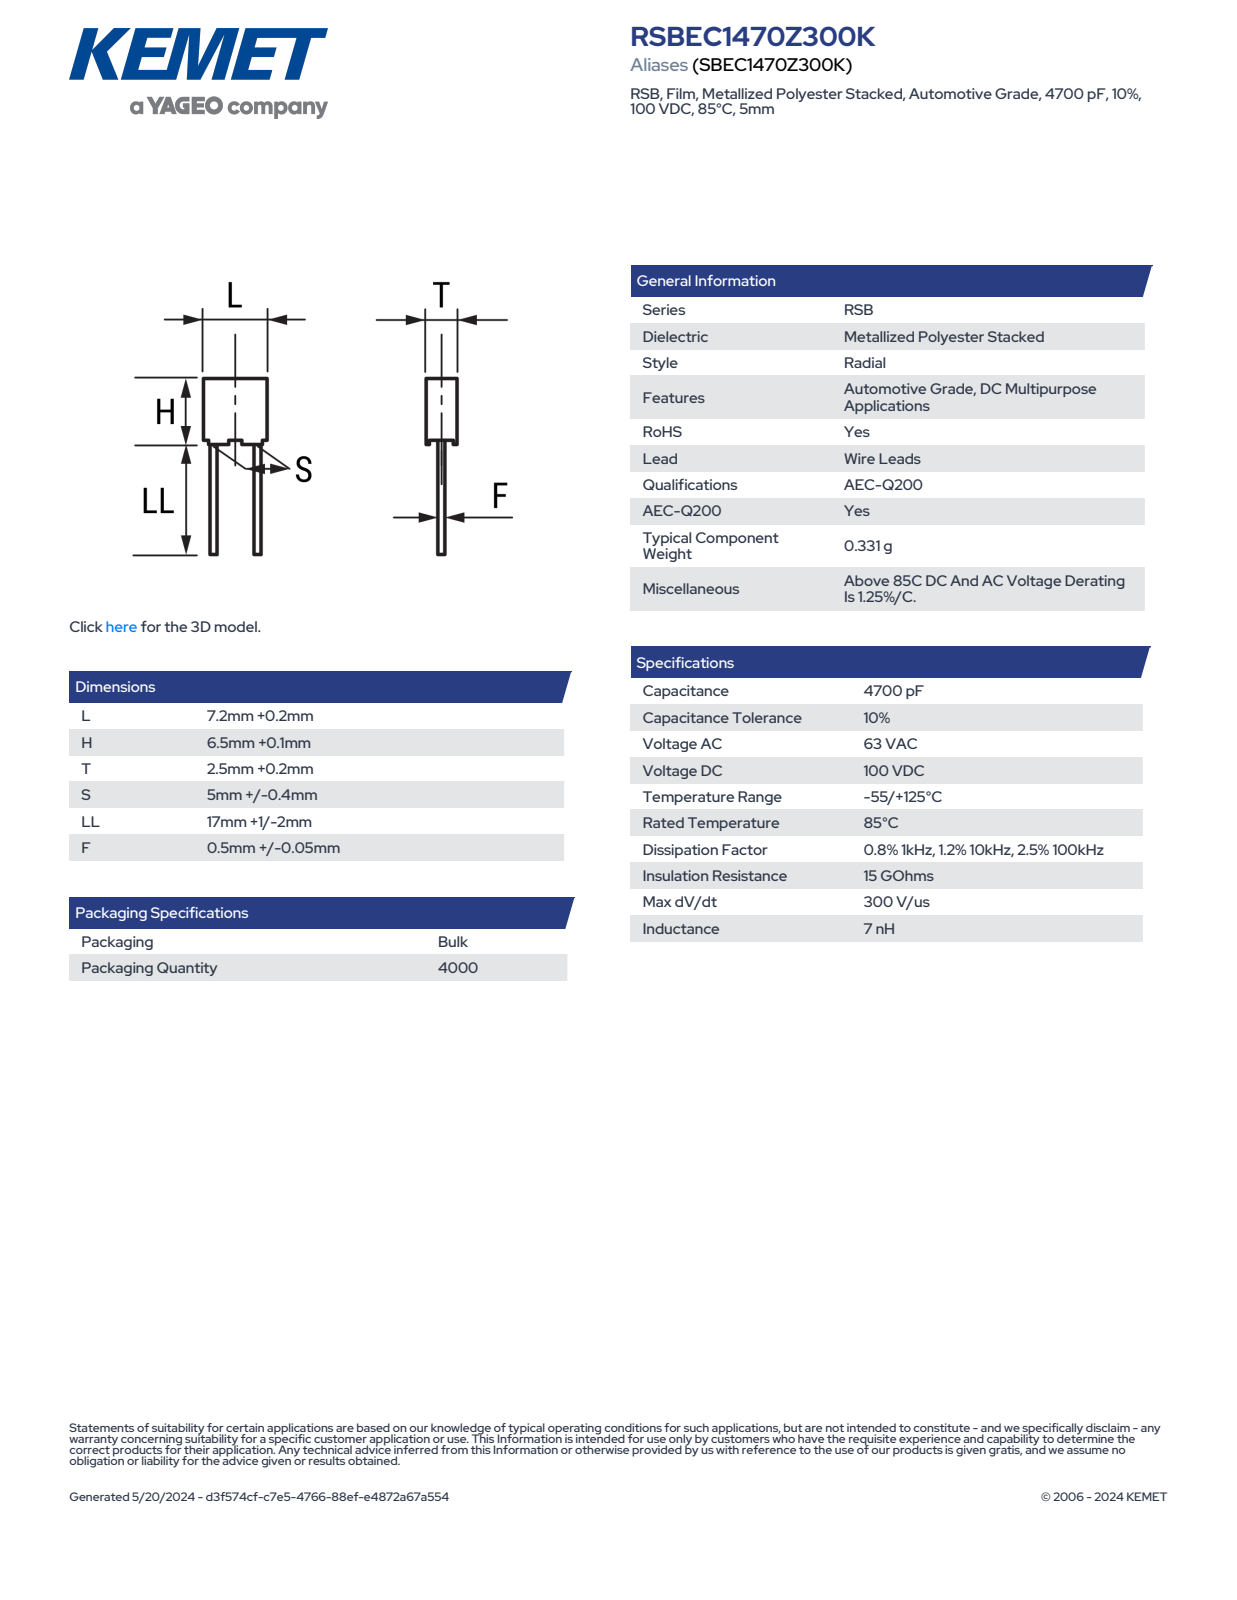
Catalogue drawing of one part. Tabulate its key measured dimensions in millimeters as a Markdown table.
| quantity | value |
| --- | --- |
| part name | CFR_RB3_7.2X6.5X2.5_L7.4H6.6T2.7S5LL18F0.65 |
| STEP written by | SolidWorks 2014 (AUTOMOTIVE_DESIGN) |
| units | millimeters |
| bodies | 4 solids, 85 faces (77 planar, 8 cylindrical, 0 other) |
| overall size | 24.6 × 7.4 × 2.71 |
| volume | 132 mm³ |
| surface area | 262 mm² |
| round bosses / shafts (diameter × count) | 0.65 × 2 |
| partial cylindrical surfaces (radius × count) | 0.5 × 4 |
| main face-to-face distances | 2.7, 7.4, 5.85, 2.45, 2.2, 0.75, 6.6, 7.15, 6.9, 2.46 |
